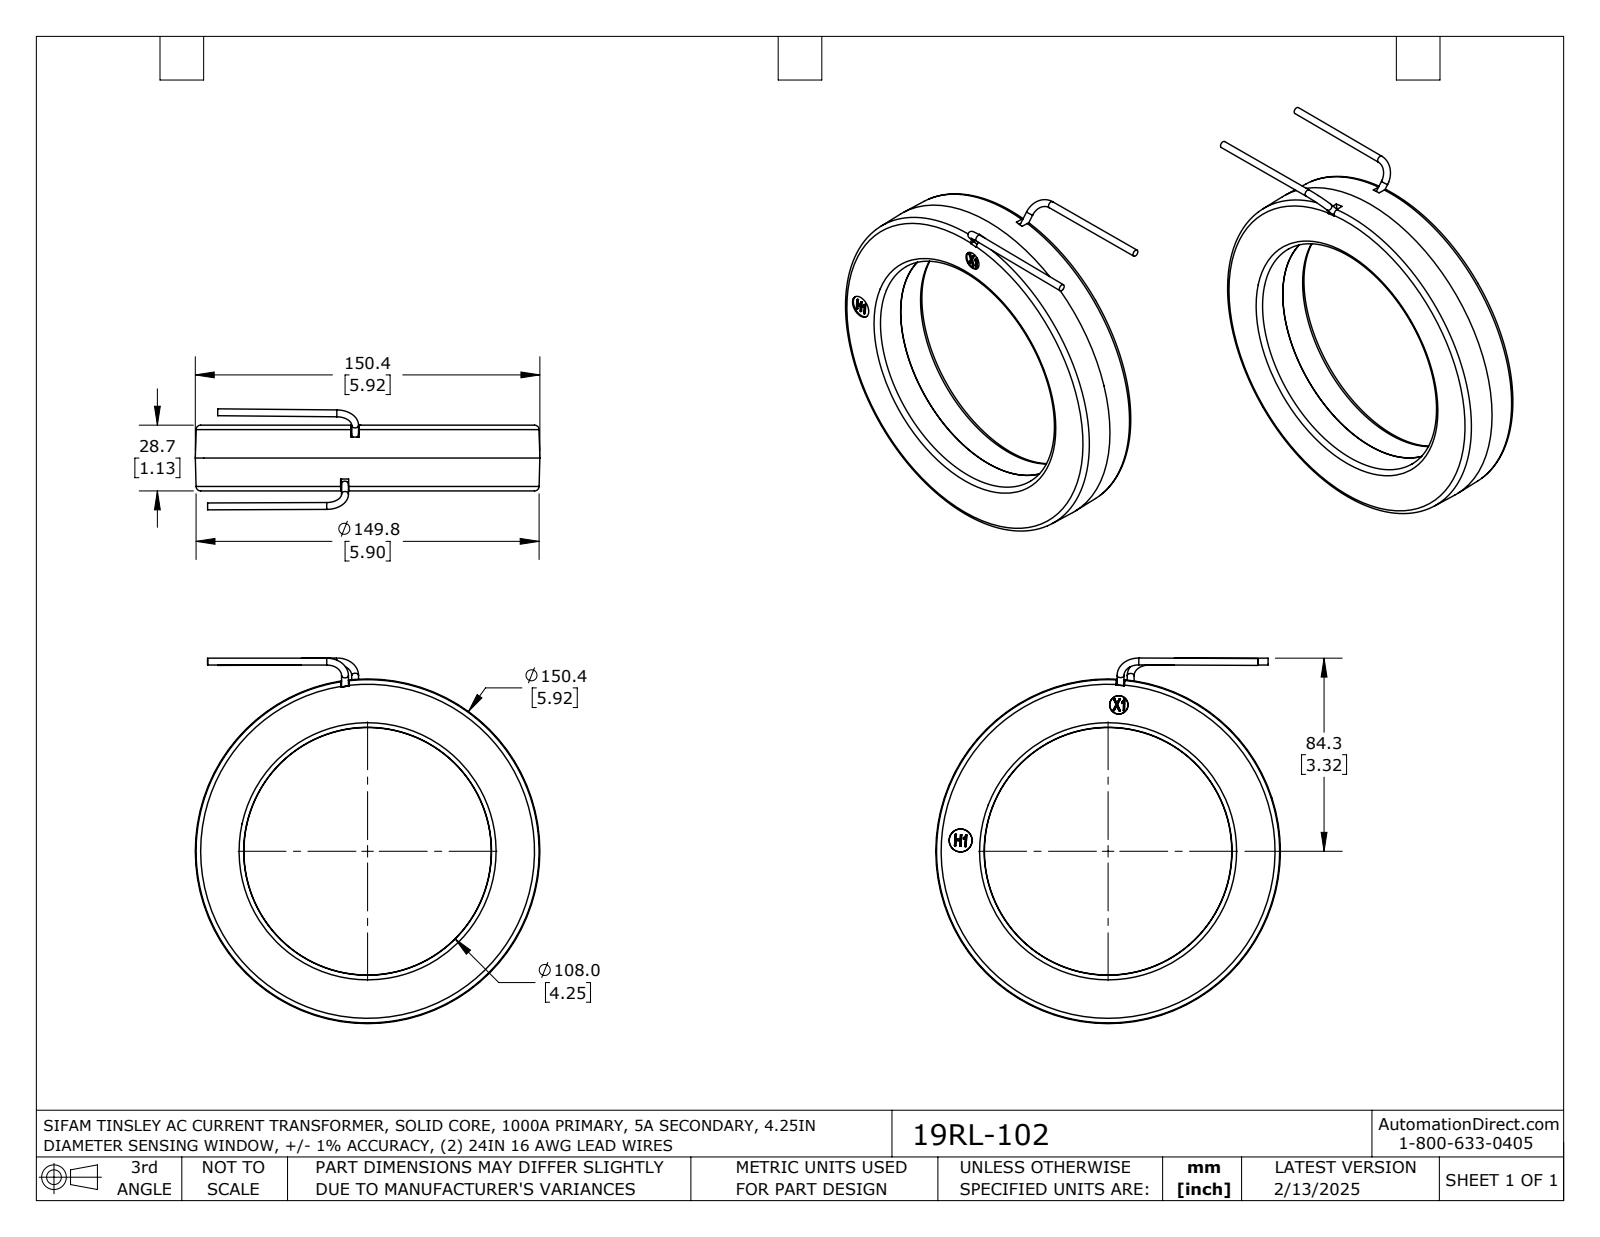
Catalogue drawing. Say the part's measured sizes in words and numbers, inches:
The part is named "19RL-102". Its 3-D file was written by "SolidWorks 2021 (AUTOMOTIVE_DESIGN)". It is 1 solid with 104 faces: 52 planar, 8 cylindrical and 44 other. Overall it measures 6.282 by 5.922 by 1.734 inches. Its volume is 14.81 cubic inches and its surface area 85.38 square inches. Round bosses or shafts: 4 of diameter 0.118. The main face-to-face distances are 0.563, 0.567, 1.13, 1.111, 0.548, 0.544, 0.019, 1.109, 0.546, 0.542.
